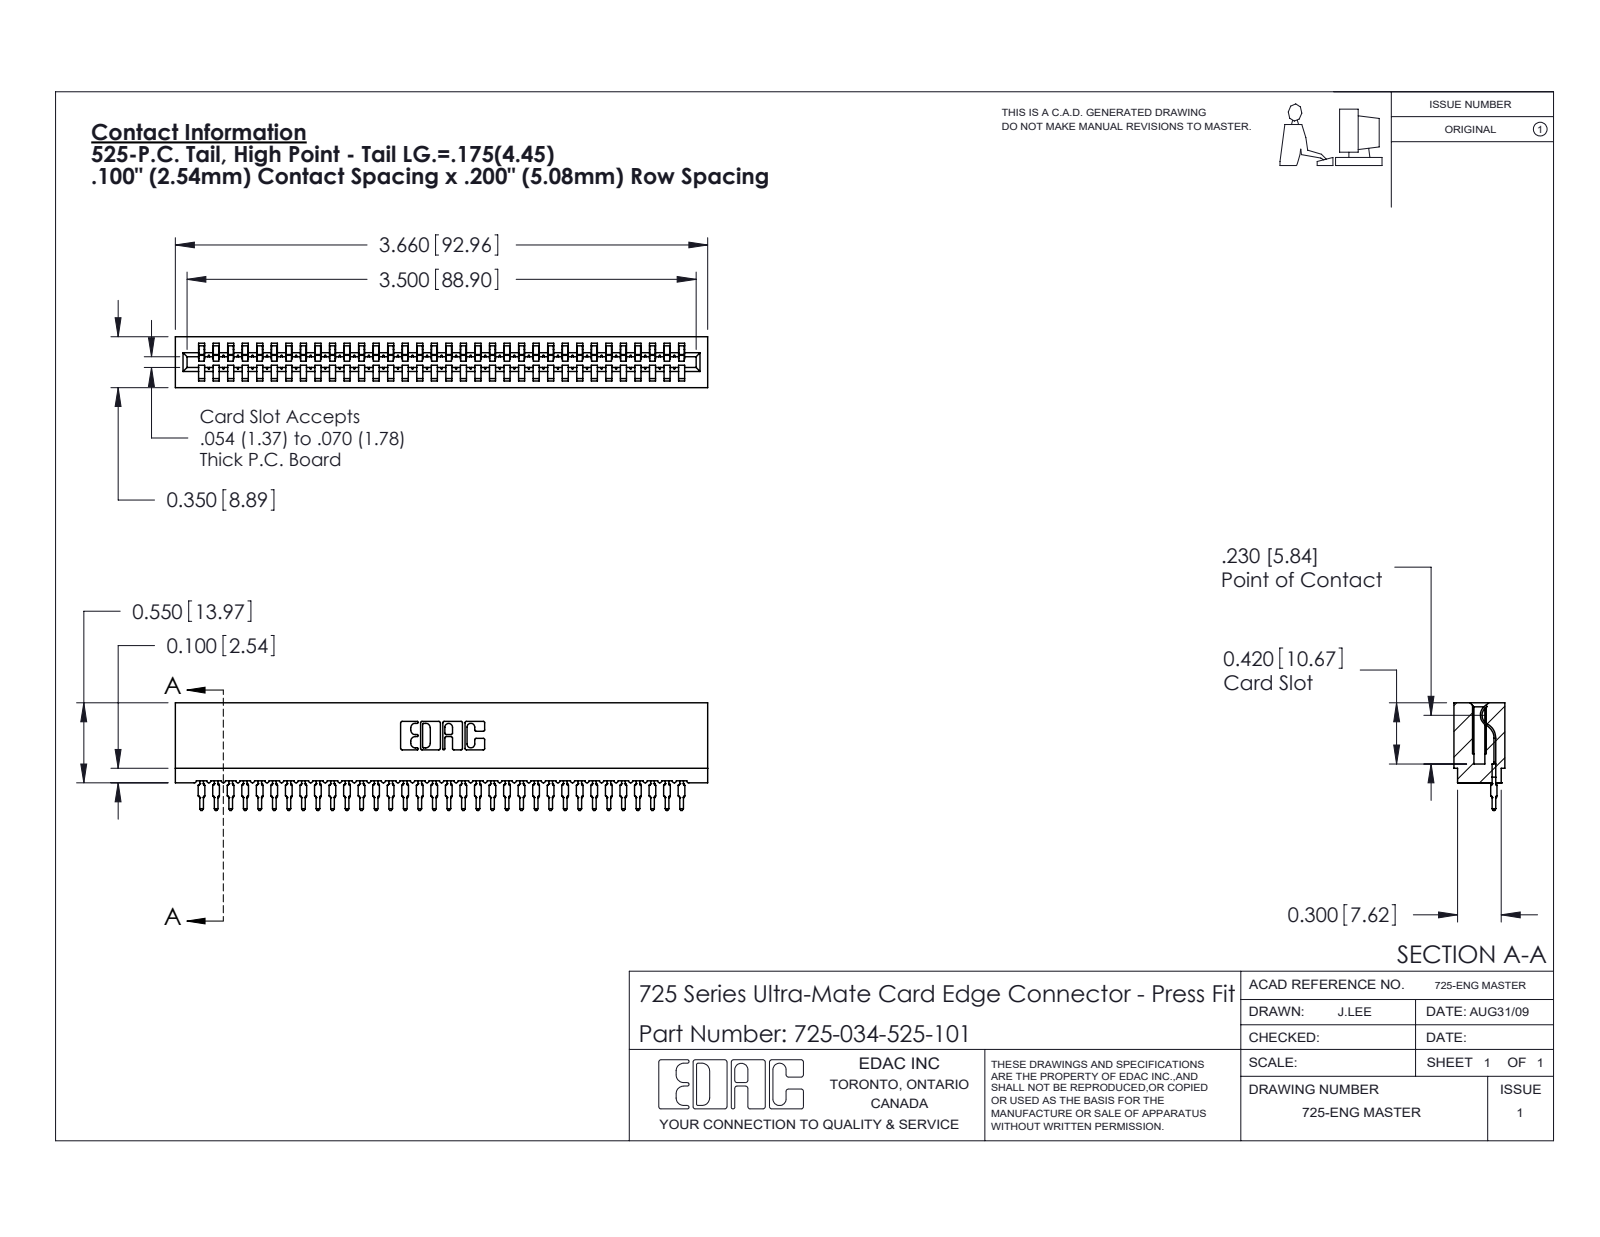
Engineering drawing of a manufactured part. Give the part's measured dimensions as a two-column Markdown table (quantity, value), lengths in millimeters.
| quantity | value |
| --- | --- |
| part name | 725 Part_Insulator Option - 01; 725-034-525-101; 745-292-001_525 |
| STEP written by | SolidWorks 2020 (CONFIG_CONTROL_DESIGN) |
| units | millimeters |
| bodies | 35 solids, 3903 faces (2333 planar, 686 cylindrical, 884 other) |
| overall size | 93 × 18.8 × 8.9 |
| volume | 7 060 mm³ |
| surface area | 13 400 mm² |
| partial cylindrical surfaces (radius × count) | 0.4 × 68, 0.5 × 68, 0.3 × 22, 0.2 × 6, 0.8 × 6, 0.1 × 4, 0.3 × 4, 0.7 × 3 |
| main face-to-face distances | 5.1, 2.5, 8.9, 7.6, 5.4, 3.5, 10.2, 12.7, 1.1, 7.7 |
